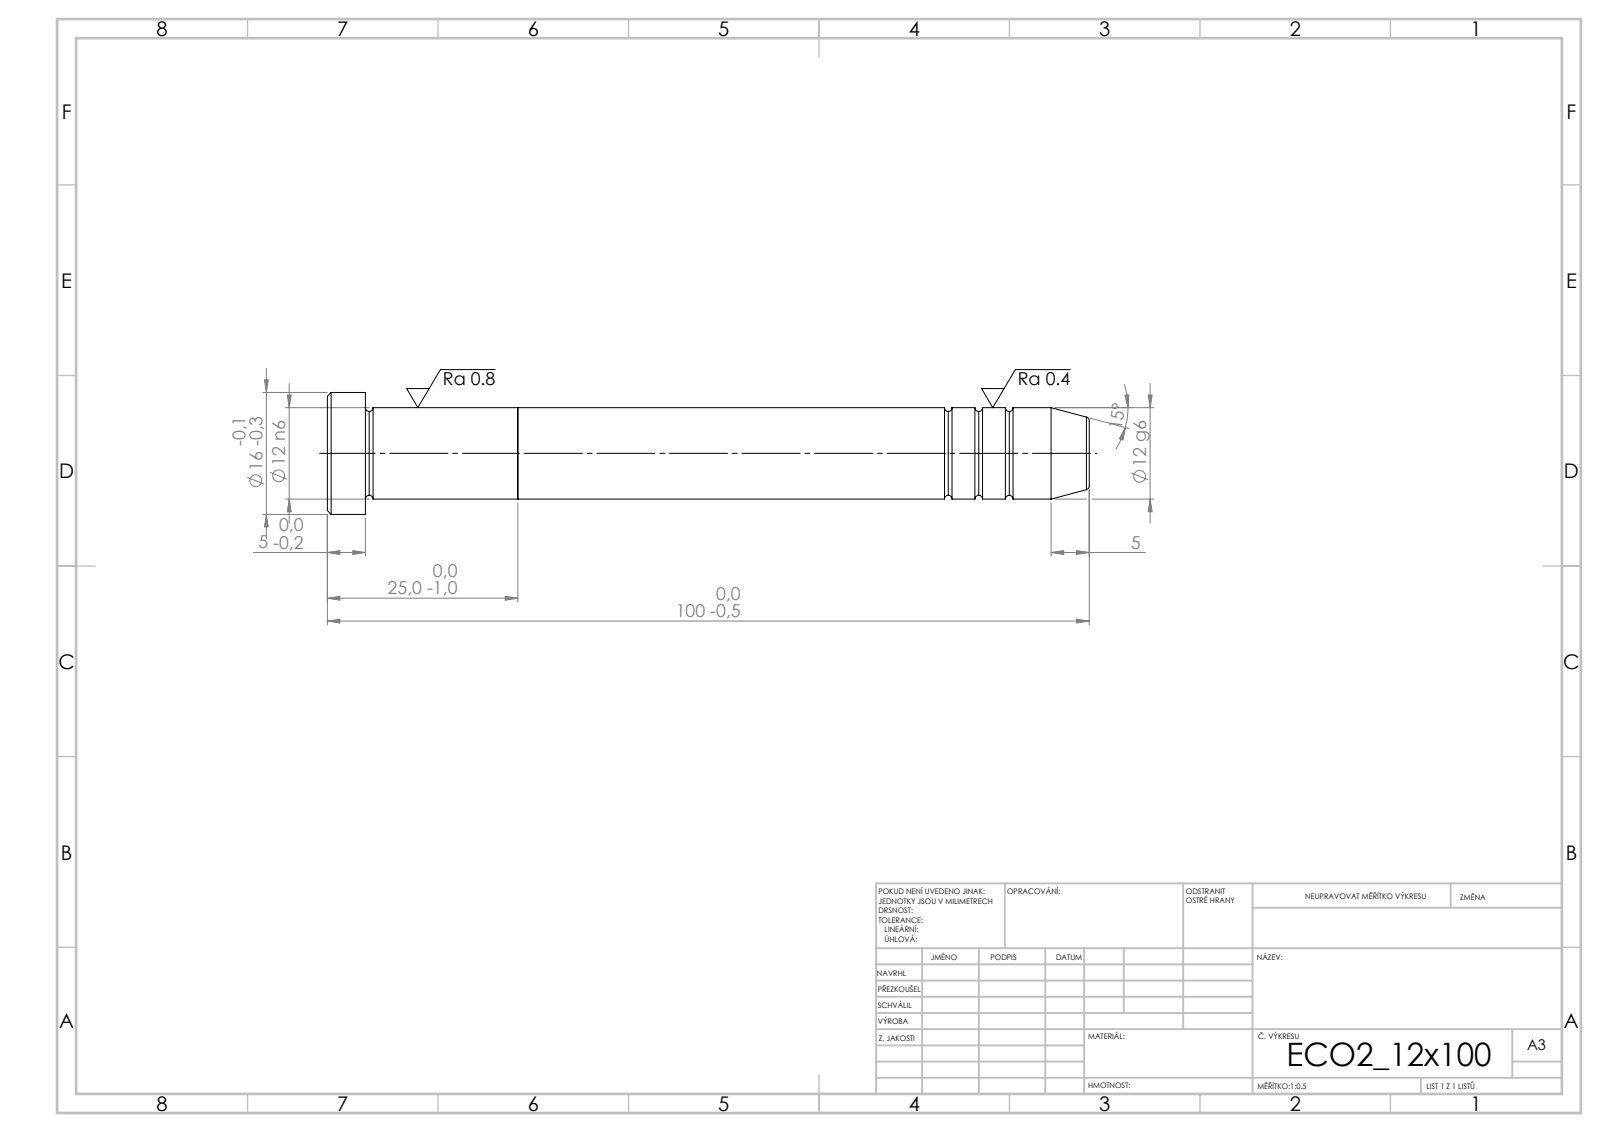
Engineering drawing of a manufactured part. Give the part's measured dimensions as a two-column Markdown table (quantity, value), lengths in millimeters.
| quantity | value |
| --- | --- |
| STEP written by | SolidWorks 2019 (CONFIG_CONTROL_DESIGN) |
| units | millimeters |
| bodies | 2 solids, 39 faces (5 planar, 12 cylindrical, 22 other) |
| overall size | 100 × 16 × 16 |
| volume | 11 569 mm³ |
| surface area | 4 456 mm² |
| round bosses / shafts (diameter × count) | 16 × 1, 12 × 1 |
| main face-to-face distances | 25, 20, 5, 75, 95, 100 |
